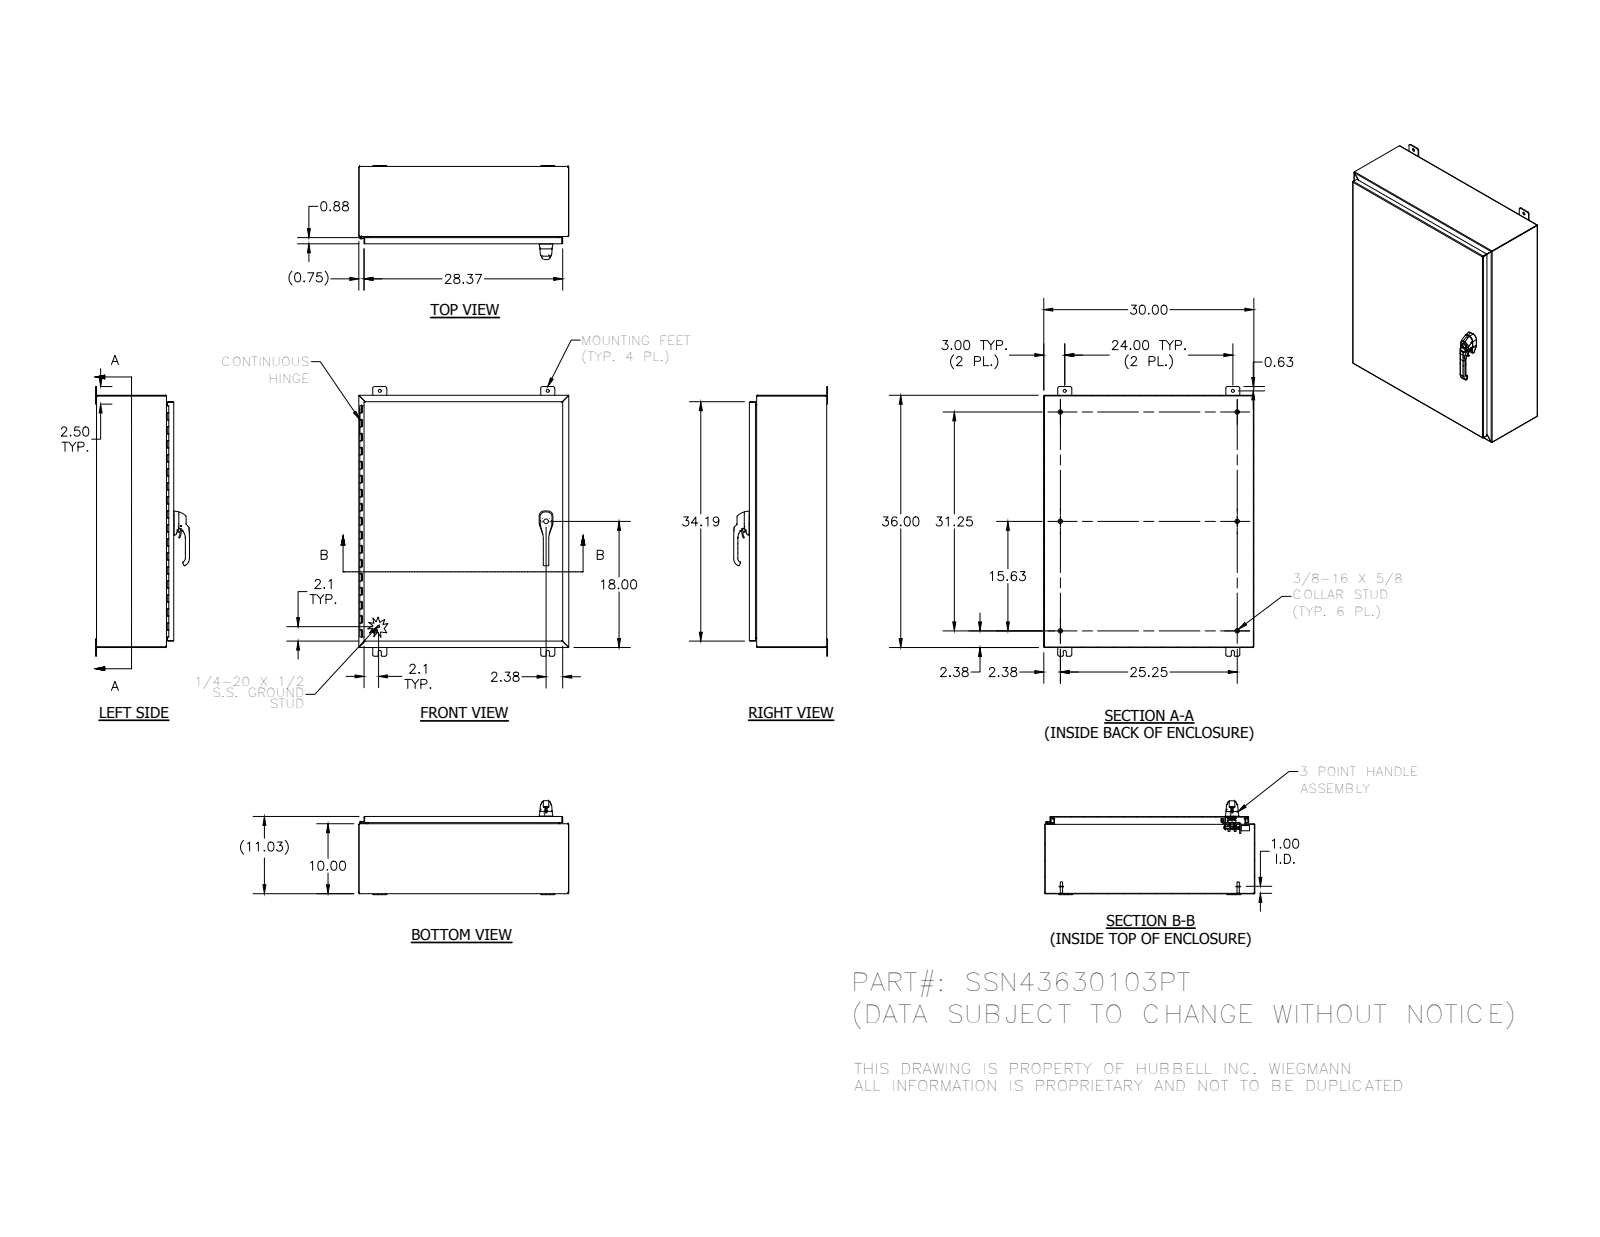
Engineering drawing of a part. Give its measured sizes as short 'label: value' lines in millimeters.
name: SUPPORT-ROLL_AF0; 1225-05; SSN43630103PTBKP; 328140P (+8 more)
written by: SolidWorks 2014 (AUTOMOTIVE_DESIGN)
unit: mm
bodies: 57 solids, 3191 faces (1086 planar, 1328 cylindrical, 777 other)
size: 977.9 × 762 × 340.6
volume: 4 892 000 mm³; area: 5 159 000 mm²
holes: 8× ⌀6.7, 4× ⌀4.7, 4× ⌀11.1, 3× ⌀5.4, 3× ⌀7.1, 2× ⌀6.1, 2× ⌀6.4, 2× ⌀6.4, 2× ⌀8, 2× ⌀10.2, 2× ⌀10.2, 2× ⌀10.5
bosses: 6× ⌀15.9, 6× ⌀8.4, 3× ⌀6, 2× ⌀25.4, 2× ⌀14.3, 2× ⌀13.5, 2× ⌀13.5, 2× ⌀12.7
rounds: 172× R0.5, 113× R0.3, 24× R0.8, 21× R0.5, 20× R2.7, 20× R6.4, 18× R3.2, 16× R0.6
face distances: 1.9, 278.4, 276.5, 280.2, 760.1, 912.5, 758.2, 762, 252.1, 26.2
hole spacings: 9.7, 12.5, 19.3, 22.5, 671.3, 5.9, 6.6, 9.7
